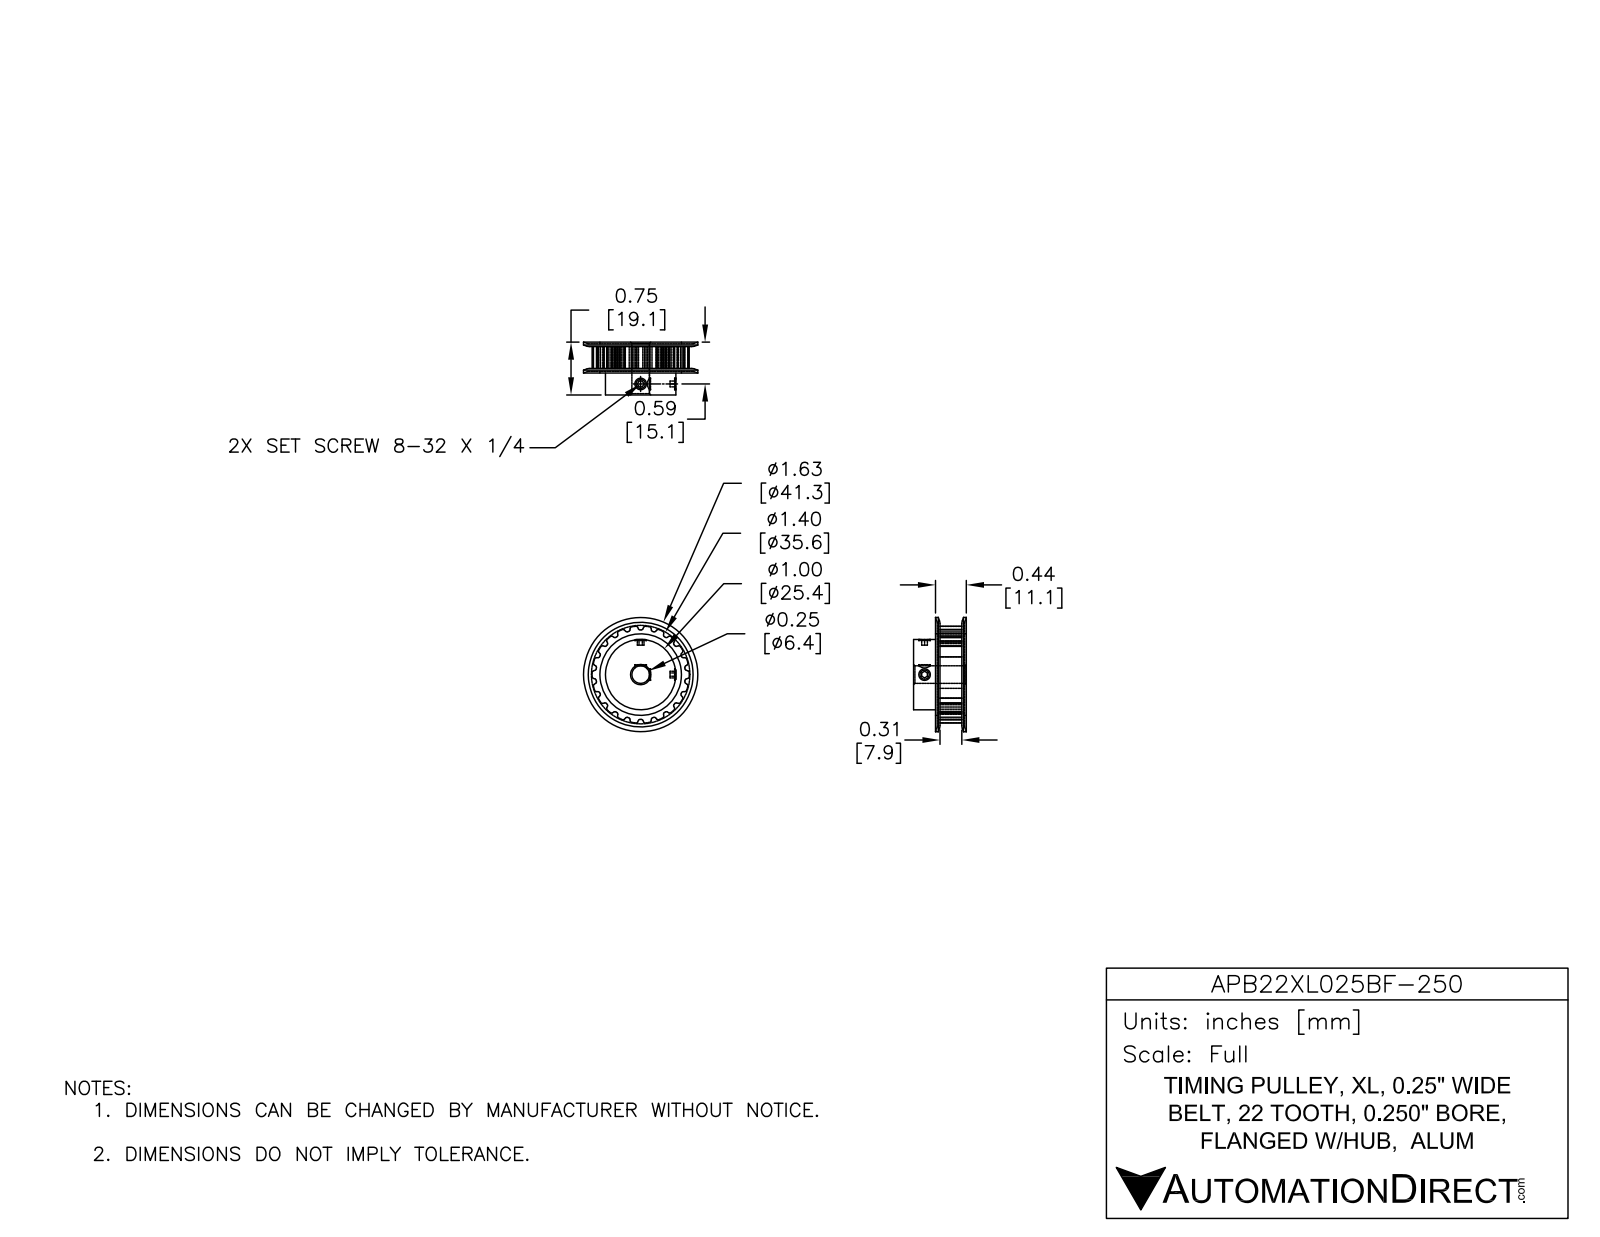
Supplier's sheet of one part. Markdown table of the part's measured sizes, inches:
| quantity | value |
| --- | --- |
| part name | APB22XL025BF-250 |
| STEP written by | SolidWorks 2014 (AUTOMOTIVE_DESIGN) |
| units | inches |
| bodies | 1 solid, 226 faces (72 planar, 132 cylindrical, 22 other) |
| overall size | 1.625 × 1.625 × 0.75 |
| volume | 0.823 in³ |
| surface area | 9.356 in² |
| round holes (diameter × count) | 0.088 × 2, 0.25 × 1 |
| round bosses / shafts (diameter × count) | 1 × 1 |
| partial cylindrical surfaces (radius × count) | 0.015 × 88, 0.636 × 1 |
| main face-to-face distances | 0.343, 0.375, 0.033, 0.407, 0.75, 0.717, 0.032, 1.381, 0.491, 0.065 |
